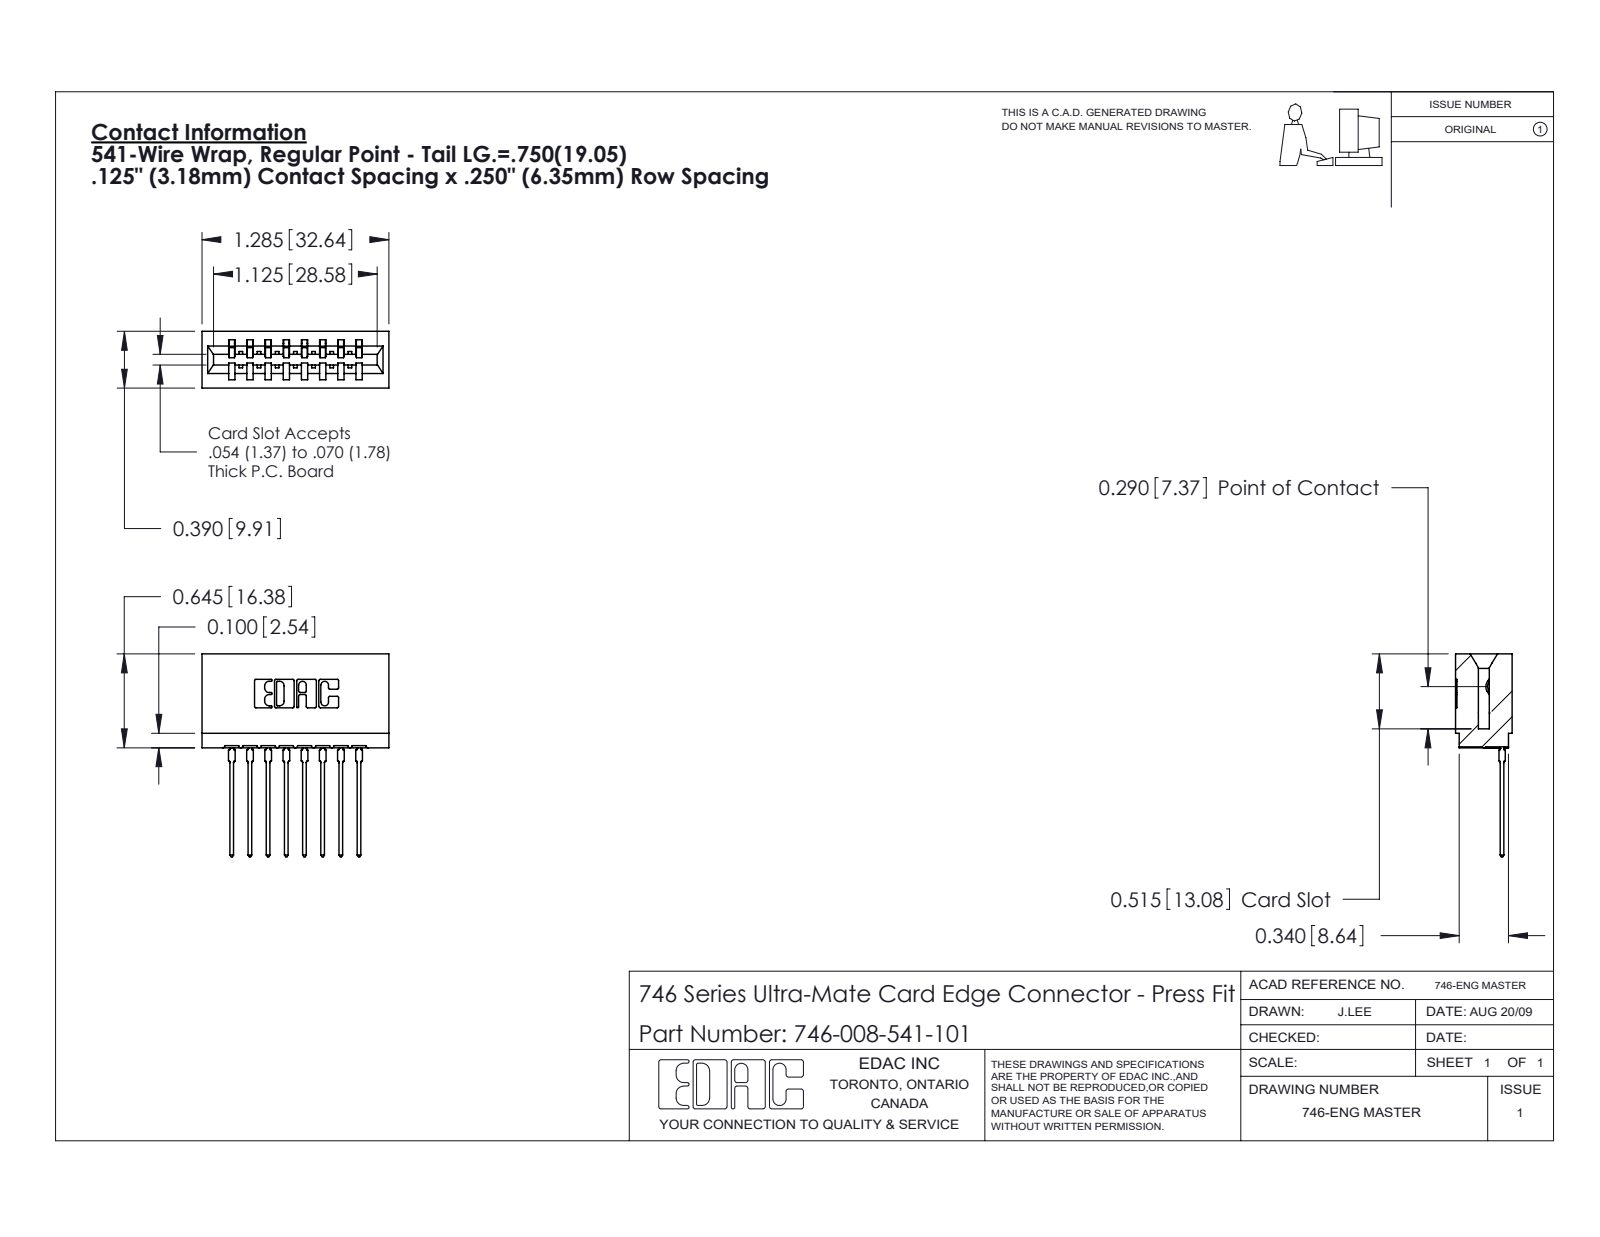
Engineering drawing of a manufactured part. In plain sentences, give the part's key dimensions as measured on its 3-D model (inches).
The part is named "746 Part_.515 Slot Depth - 01; 746-292-001_541; 746-008-541-101". Its 3-D file was written by "SolidWorks 2020 (CONFIG_CONTROL_DESIGN)". It is 9 solids with 961 faces: 559 planar, 194 cylindrical and 208 other. Overall it measures 1.394 by 1.285 by 0.39 inches. Its volume is 0.225 cubic inches and its surface area 7.868 square inches. Partial cylindrical surfaces (rounded edges, fillets, slot ends): 22 of radius 0.01, 16 of radius 0.021, 9 of radius 0.015, 6 of radius 0.007, 6 of radius 0.031, 4 of radius 0.005, 4 of radius 0.011, 3 of radius 0.026. The main face-to-face distances are 0.25, 0.042, 0.125, 0.5, 0.333, 0.057, 0.292, 0.208, 0.375, 0.125.
